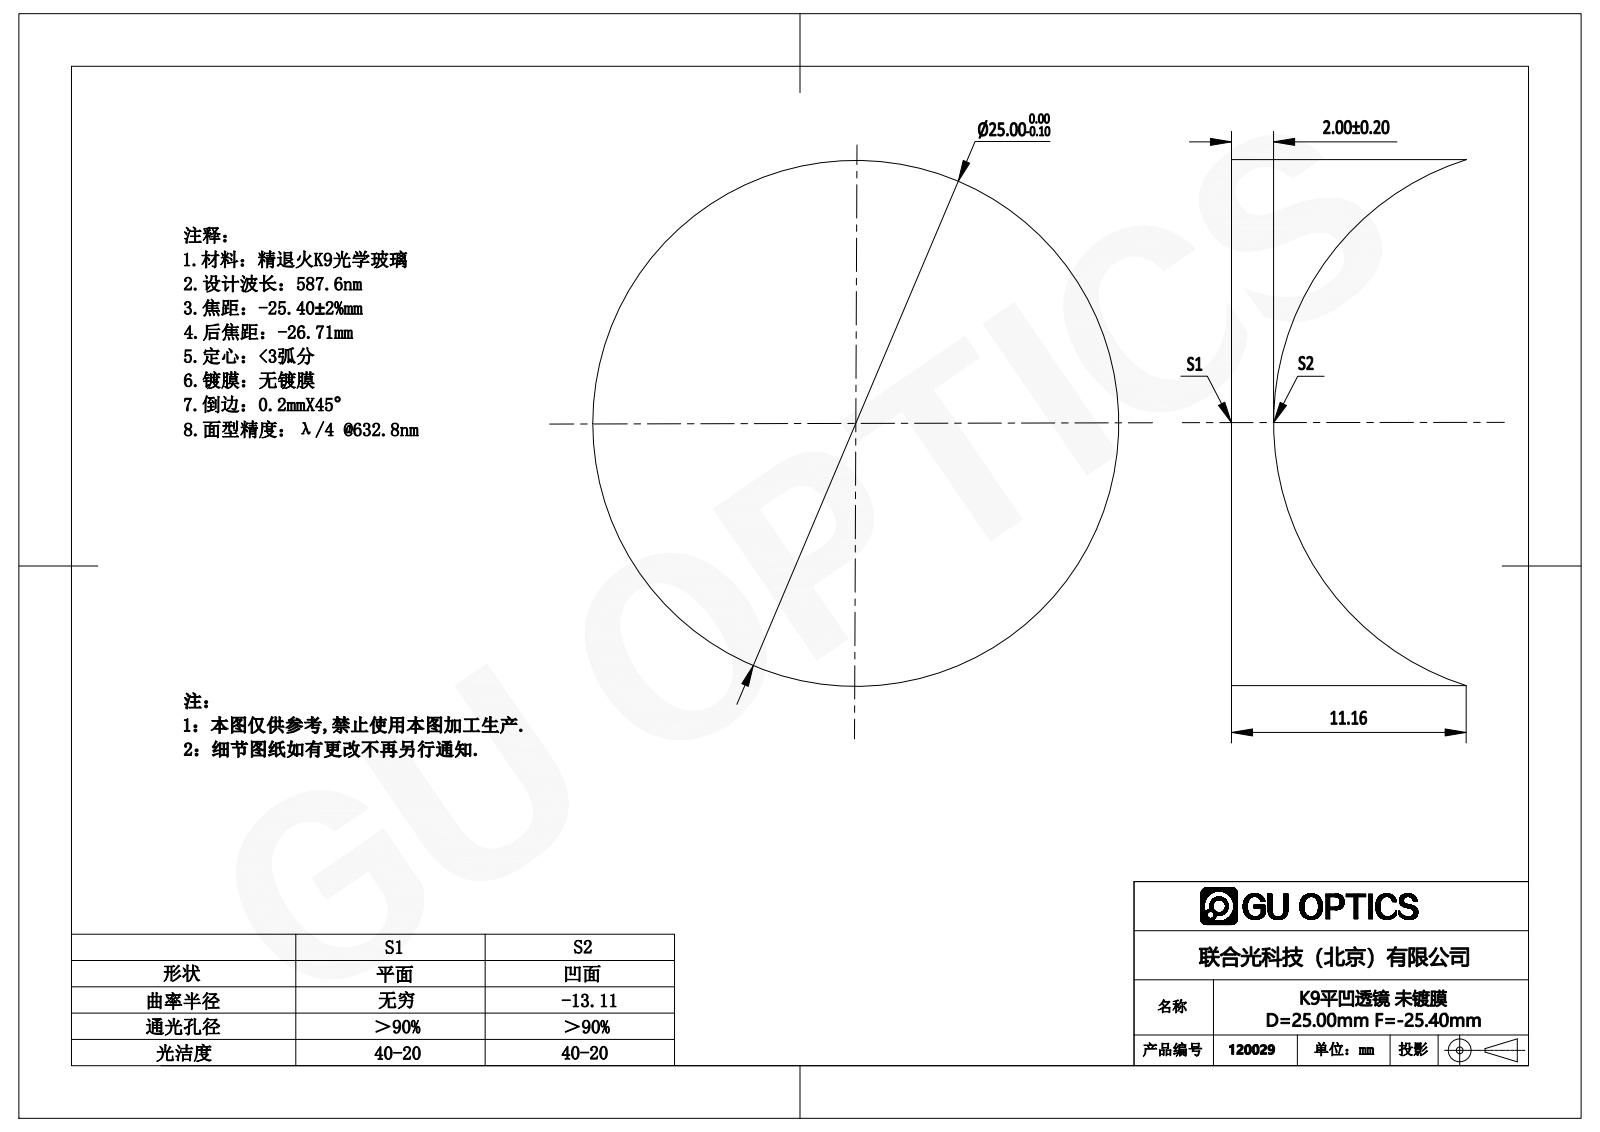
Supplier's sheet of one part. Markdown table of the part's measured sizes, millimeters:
| quantity | value |
| --- | --- |
| part name | 120029 |
| STEP written by | SolidWorks 2016 (AUTOMOTIVE_DESIGN) |
| units | millimeters |
| bodies | 1 solid, 5 faces (1 planar, 2 cylindrical, 2 other) |
| overall size | 25 × 25 × 11.16 |
| volume | 2 828 mm³ |
| surface area | 2 122 mm² |
| round bosses / shafts (diameter × count) | 25 × 1 |
